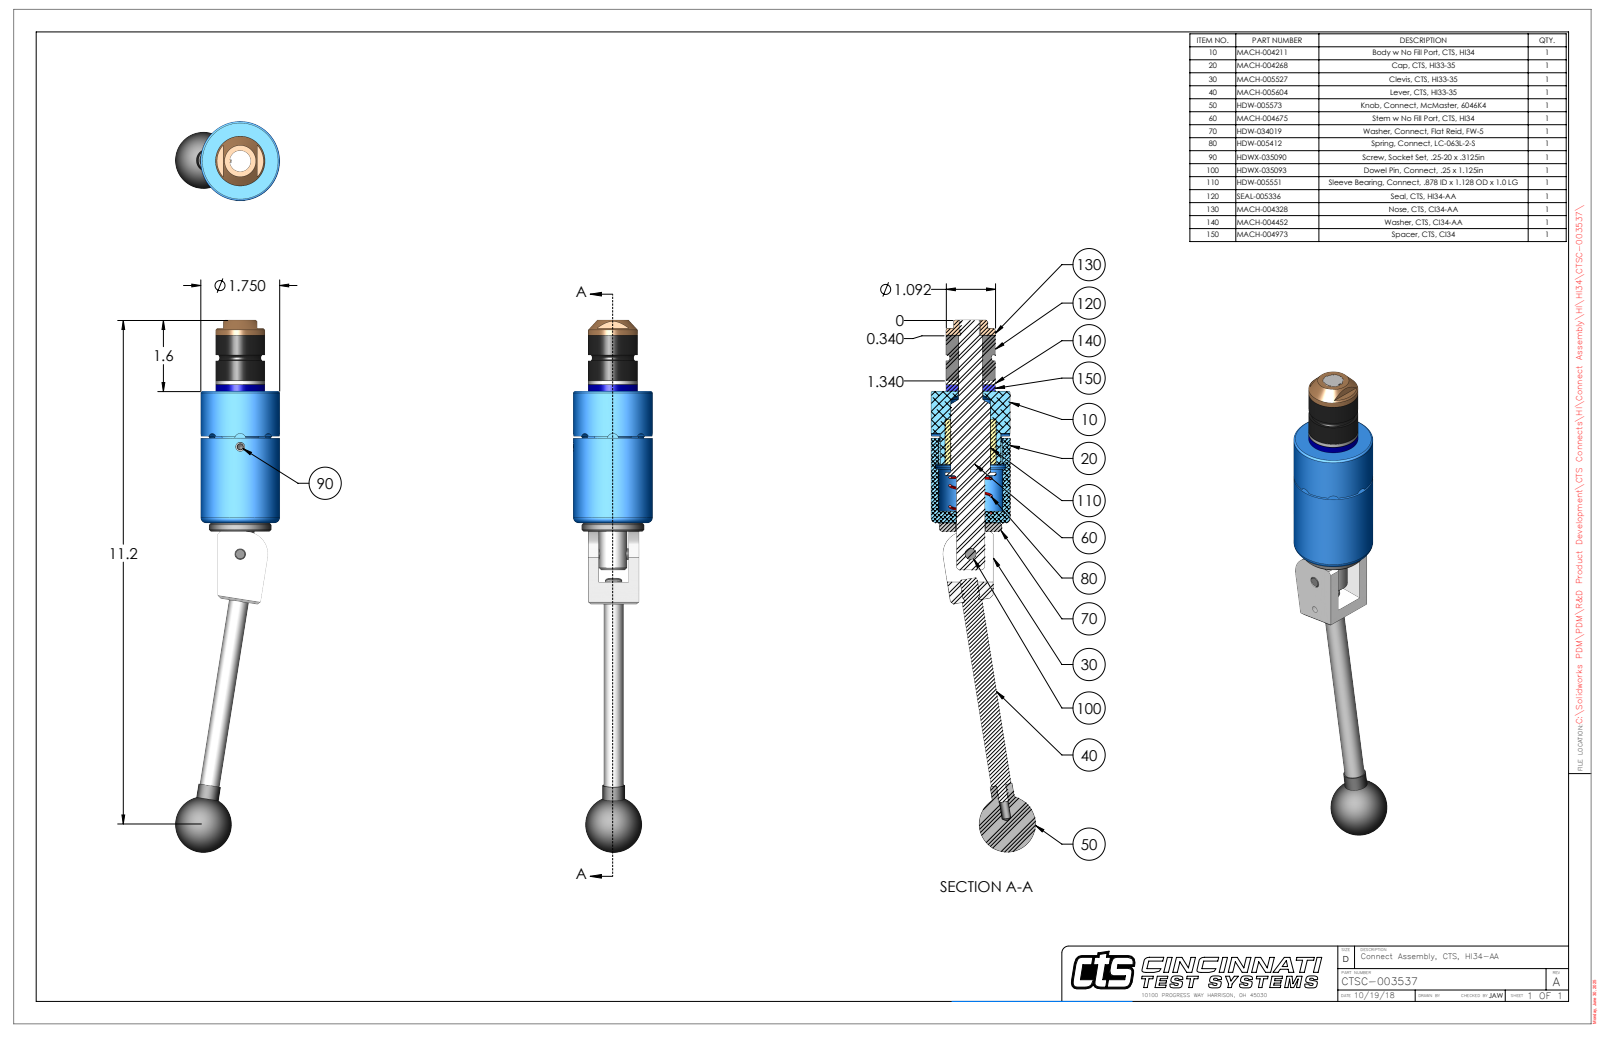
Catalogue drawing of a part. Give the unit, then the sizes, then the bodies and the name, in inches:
Units: inches
Overall size (bounding box): 11.792 × 2.312 × 1.75
Round holes (diameter × count): ⌀0.201 ×2, ⌀0.15 ×1, ⌀0.249 ×1, ⌀0.251 ×1, ⌀0.313 ×1, ⌀0.422 ×1, ⌀0.53 ×1, ⌀0.541 ×1, ⌀0.547 ×1, ⌀0.635 ×1, ⌀0.656 ×1, ⌀1.419 ×1
Round bosses / shafts (diameter × count): ⌀0.5 ×2, ⌀0.44 ×2, ⌀0.25 ×2, ⌀1.75 ×1, ⌀1.38 ×1, ⌀1.092 ×1, ⌀1.09 ×1, ⌀0.625 ×1
Partial cylindrical surfaces — rounded edges, fillets, slot ends (radius × count): R0.125 ×4, R0.029 ×2, R0.5 ×1, R0.695 ×1, R0.803 ×1
Main face-to-face distances: 2.918, 1.237, 1, 4.155, 1.12, 0.237, 3.155, 1.094, 0.094, 0.143
Hole centre spacings: 0.74, 2.376, 3.116
Volume: 11.56 in³ · Surface area: 68.86 in²
Bodies: 10 solids, 255 faces (93 planar, 103 cylindrical, 59 other)
Part name (STEP PRODUCT): CTSC-003537
STEP written by: SolidWorks 2023 (AUTOMOTIVE_DESIGN)
